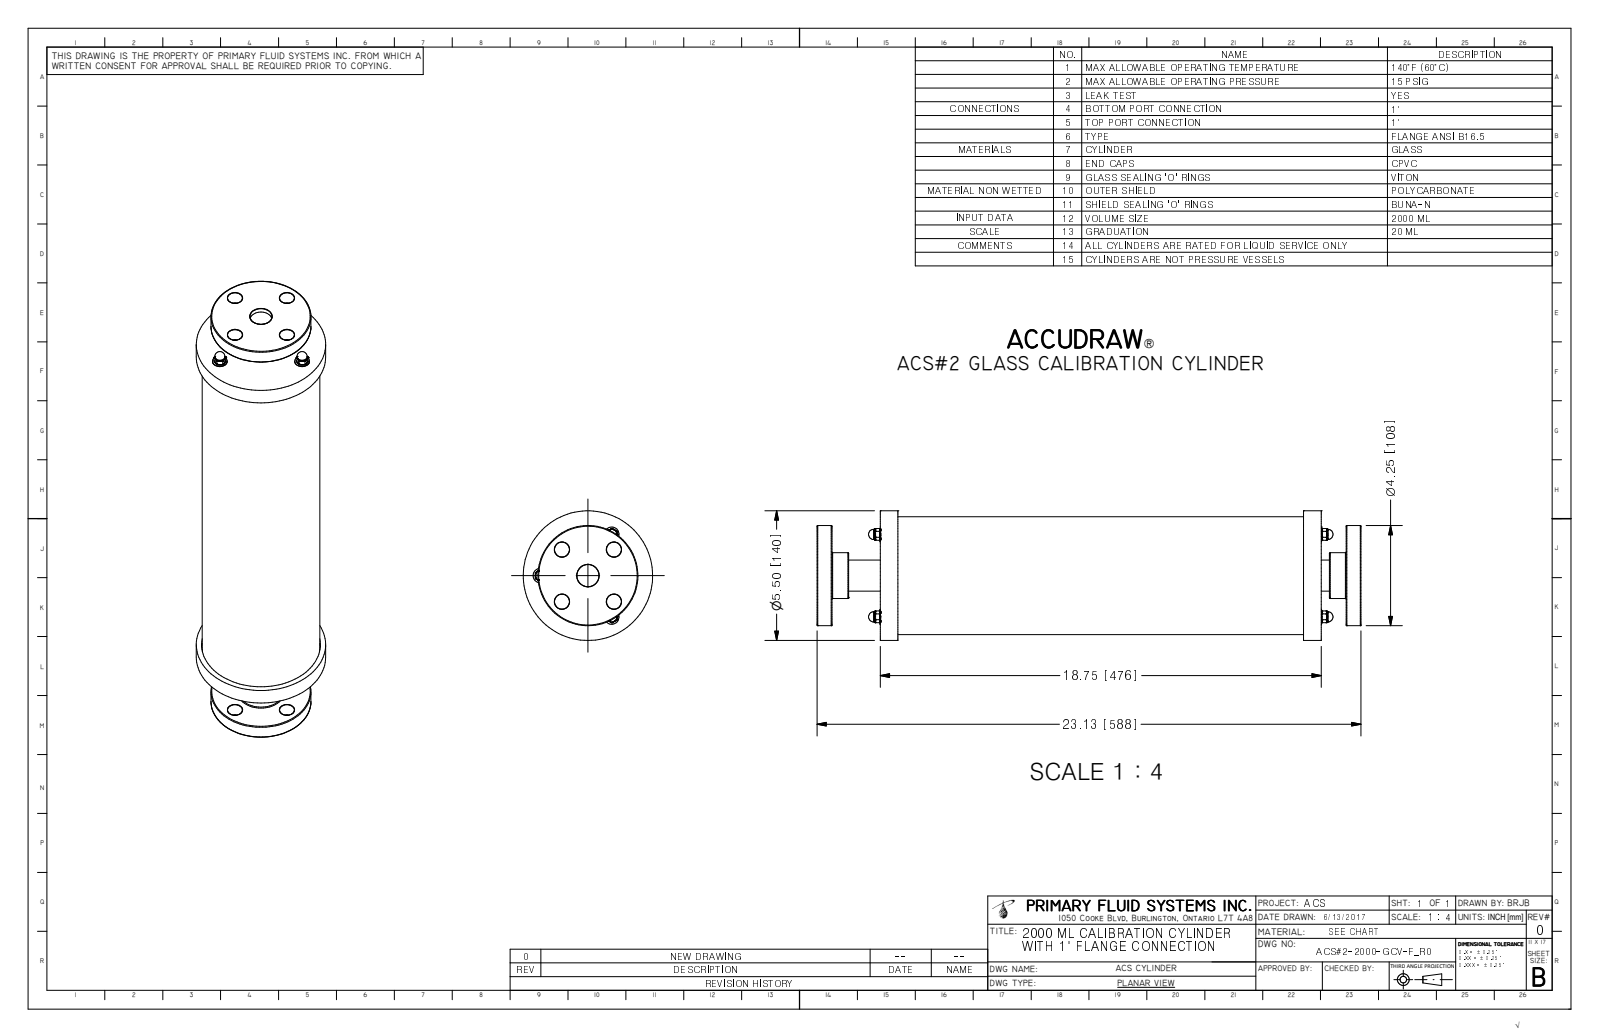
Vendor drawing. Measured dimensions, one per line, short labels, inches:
name: ACS#2-2000-GCV-F_R0
written by: Autodesk Inventor 2009 (AUTOMOTIVE_DESIGN)
unit: in
bodies: 1 solid, 619 faces (41 planar, 159 cylindrical, 419 other)
size: 23.13 × 5.5 × 5.5
volume: 107.1 in³; area: 1 194 in²
holes: 4× ⌀0.63, 3× ⌀0.18, 3× ⌀0.266, 3× ⌀0.281, 1× ⌀0.936, 1× ⌀0.957, 1× ⌀3.15, 1× ⌀3.4, 1× ⌀4.75, 1× ⌀5.05
bosses: 3× ⌀0.625, 3× ⌀0.25, 1× ⌀5.5, 1× ⌀5, 1× ⌀4.7, 1× ⌀4.25, 1× ⌀3.346, 1× ⌀3.1
face distances: 0.75, 18, 18.75, 0.635, 22.495, 17.25, 2.69, 3.44, 20.69, 21.44
hole spacings: 1.562, 2.209, 2.019, 3.497, 0.651, 1.434, 2.21, 2.855
